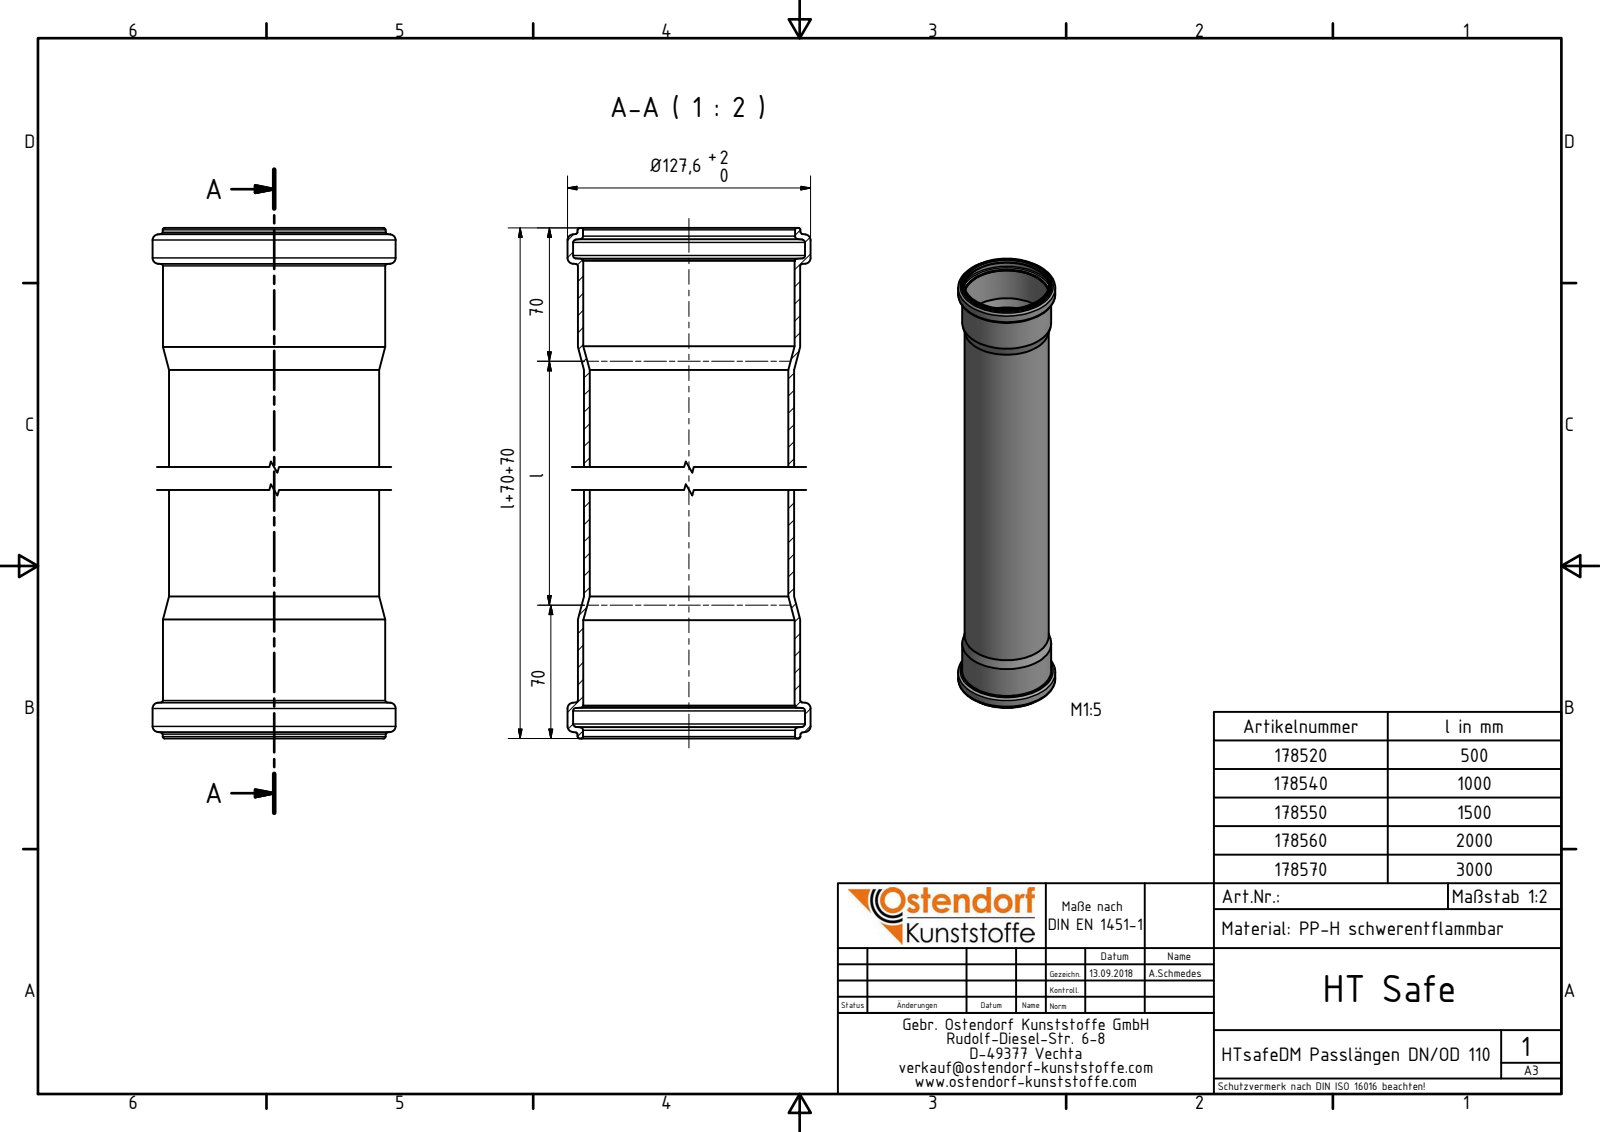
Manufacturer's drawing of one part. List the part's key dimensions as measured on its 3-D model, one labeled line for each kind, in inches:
Part name (STEP PRODUCT): 178560 HTsafeDM DN_OD 110x2000
STEP written by: Autodesk Inventor 2016 (AUTOMOTIVE_DESIGN)
Units: inches
Bodies: 1 solid, 52 faces (4 planar, 16 cylindrical, 32 other)
Overall size (bounding box): 84.252 × 5.024 × 5.024
Volume: 133.6 in³ · Surface area: 2 268 in²
Round holes (diameter × count): ⌀4.106 ×1, ⌀4.37 ×1, ⌀4.382 ×1, ⌀4.795 ×1
Round bosses / shafts (diameter × count): ⌀5.024 ×1, ⌀4.61 ×1, ⌀4.598 ×1, ⌀4.343 ×1
Main face-to-face distances: 84.252, 0.682, 83.57, 82.887
